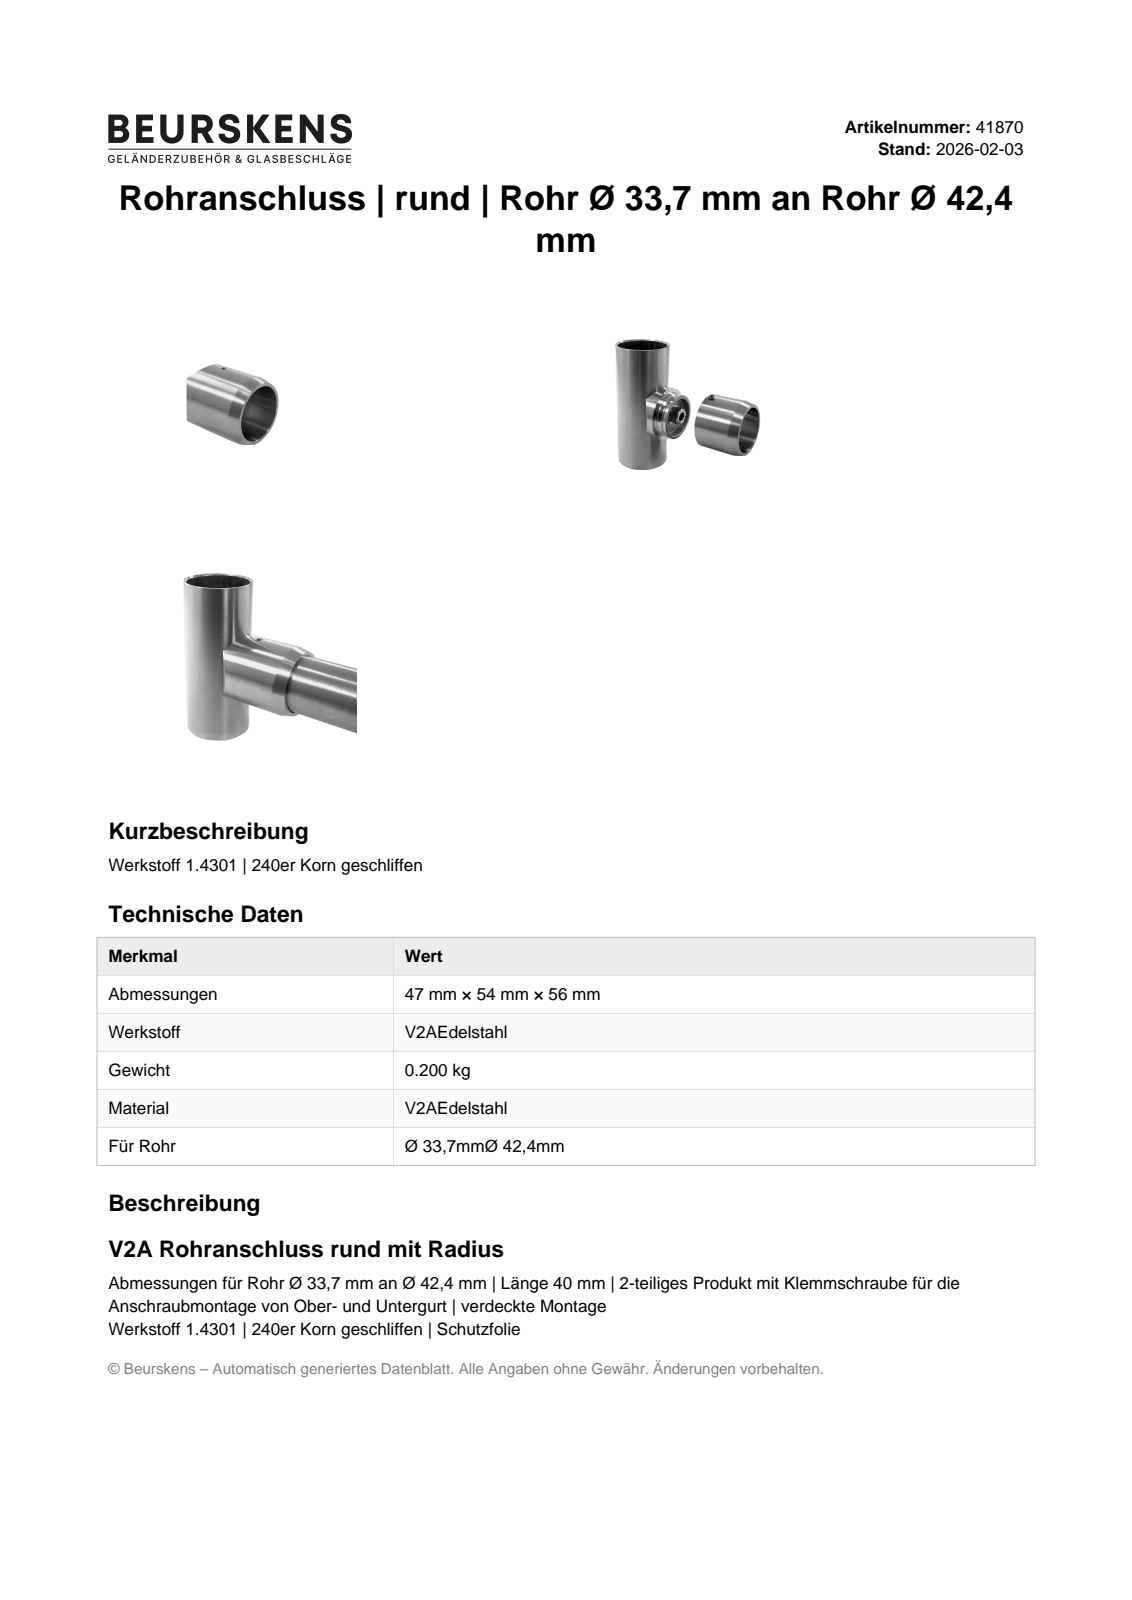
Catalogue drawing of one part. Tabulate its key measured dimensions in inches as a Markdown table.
| quantity | value |
| --- | --- |
| part name | 41870; 41870_01; 41870_02; DIN 913 - M5 x 5 |
| STEP written by | Autodesk Inventor 2022 (AUTOMOTIVE_DESIGN) |
| units | inches |
| bodies | 5 solids, 68 faces (37 planar, 15 cylindrical, 16 other) |
| overall size | 1.72 × 1.675 × 1.654 |
| volume | 1.681 in³ |
| surface area | 23.52 in² |
| round holes (diameter × count) | 0.189 × 2, 0.433 × 1, 1.142 × 1, 1.339 × 1 |
| round bosses / shafts (diameter × count) | 0.197 × 2, 1.654 × 1, 1.378 × 1 |
| partial cylindrical surfaces (radius × count) | 1.669 × 1 |
| main face-to-face distances | 0.193, 0.157, 0.35, 0.543, 0.386, 1.535, 1.378, 1.185, 0.992, 1.048 |
| hole center spacings | 0.787 |
